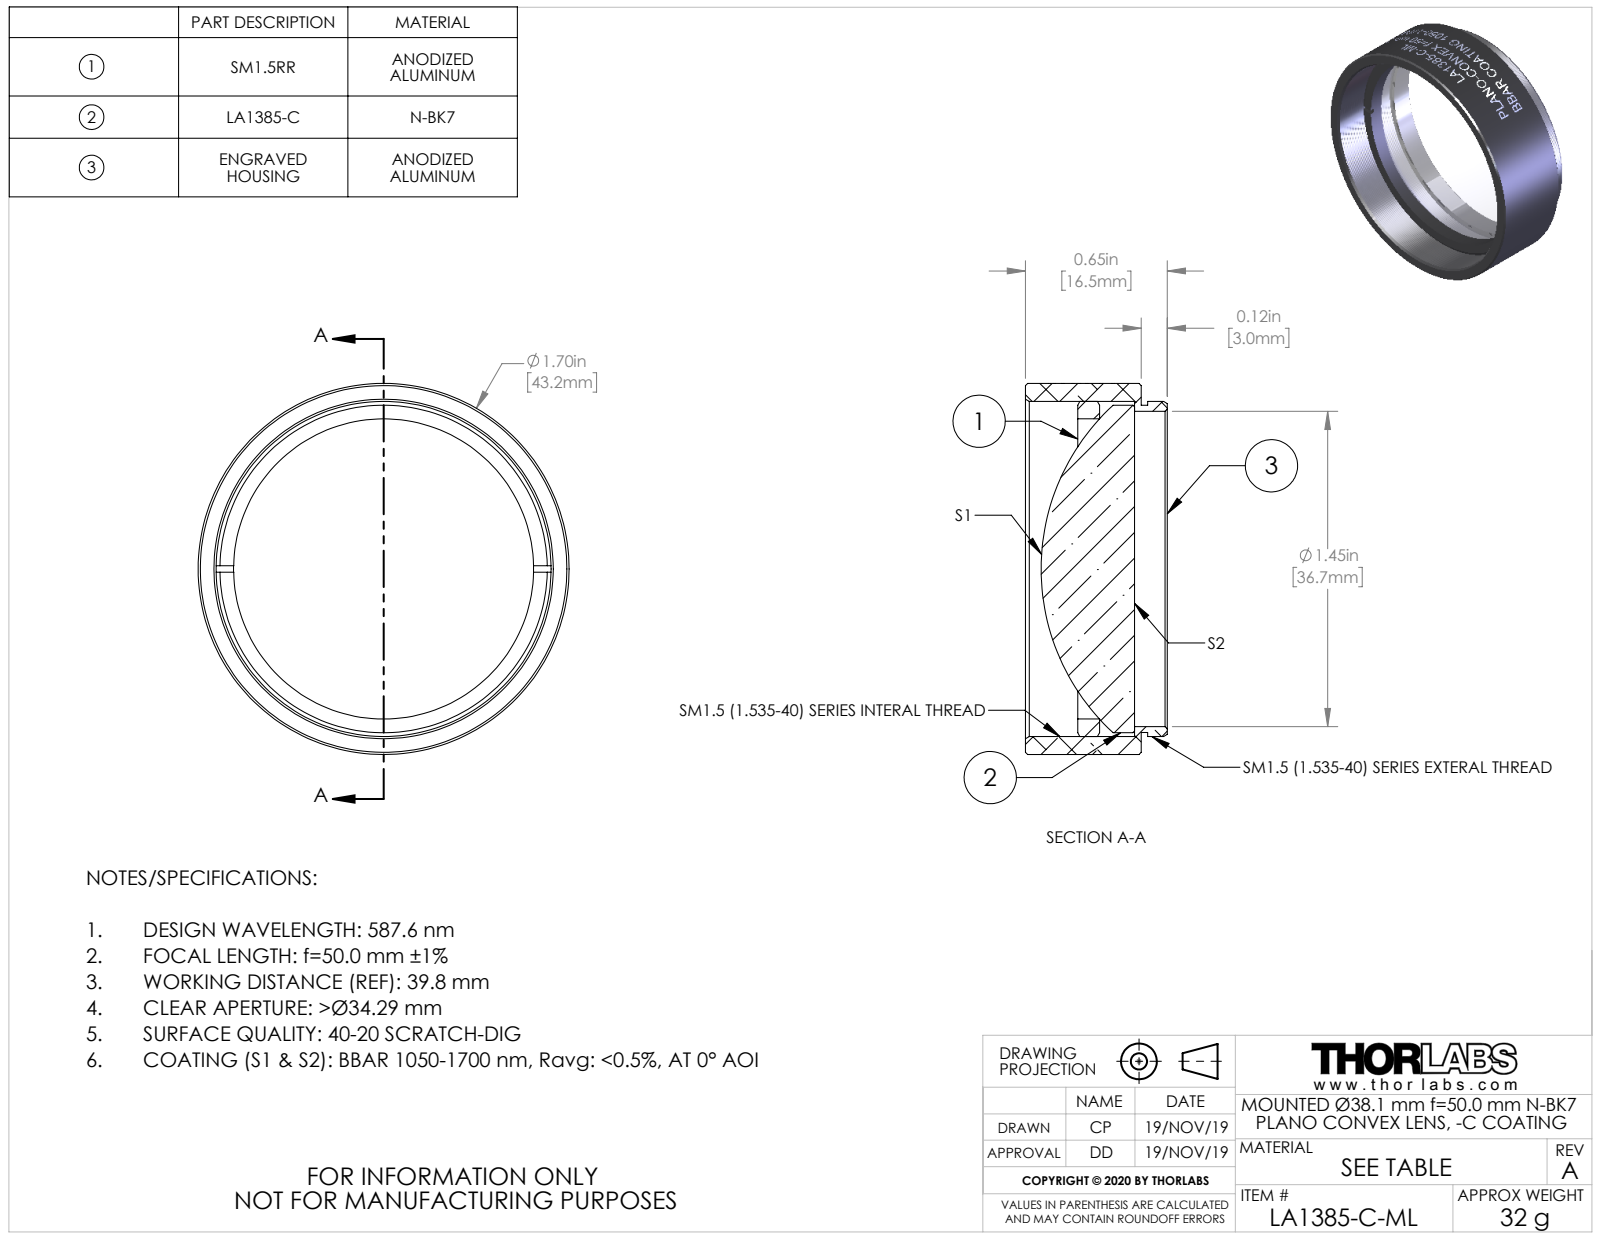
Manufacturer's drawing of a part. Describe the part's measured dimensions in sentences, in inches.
The part is named "TTN200744-E0W". Its 3-D file was written by "SolidWorks 2018 (CONFIG_CONTROL_DESIGN)". It is 3 solids with 156 faces: 15 planar, 122 cylindrical and 19 other. Overall it measures 1.7 by 1.7 by 0.65 inches. Its volume is 0.769 cubic inches and its surface area 13.67 square inches. Round holes: 1 of diameter 1.375, 1 of diameter 1.445. Round bosses or shafts: 1 of diameter 1.7, 1 of diameter 1.535, 1 of diameter 1.5, 1 of diameter 1.499. The main face-to-face distances are 0.03, 0.53, 0.5, 0.191, 0.161, 0.339, 0.291, 0.261, 0.1, 0.239.
